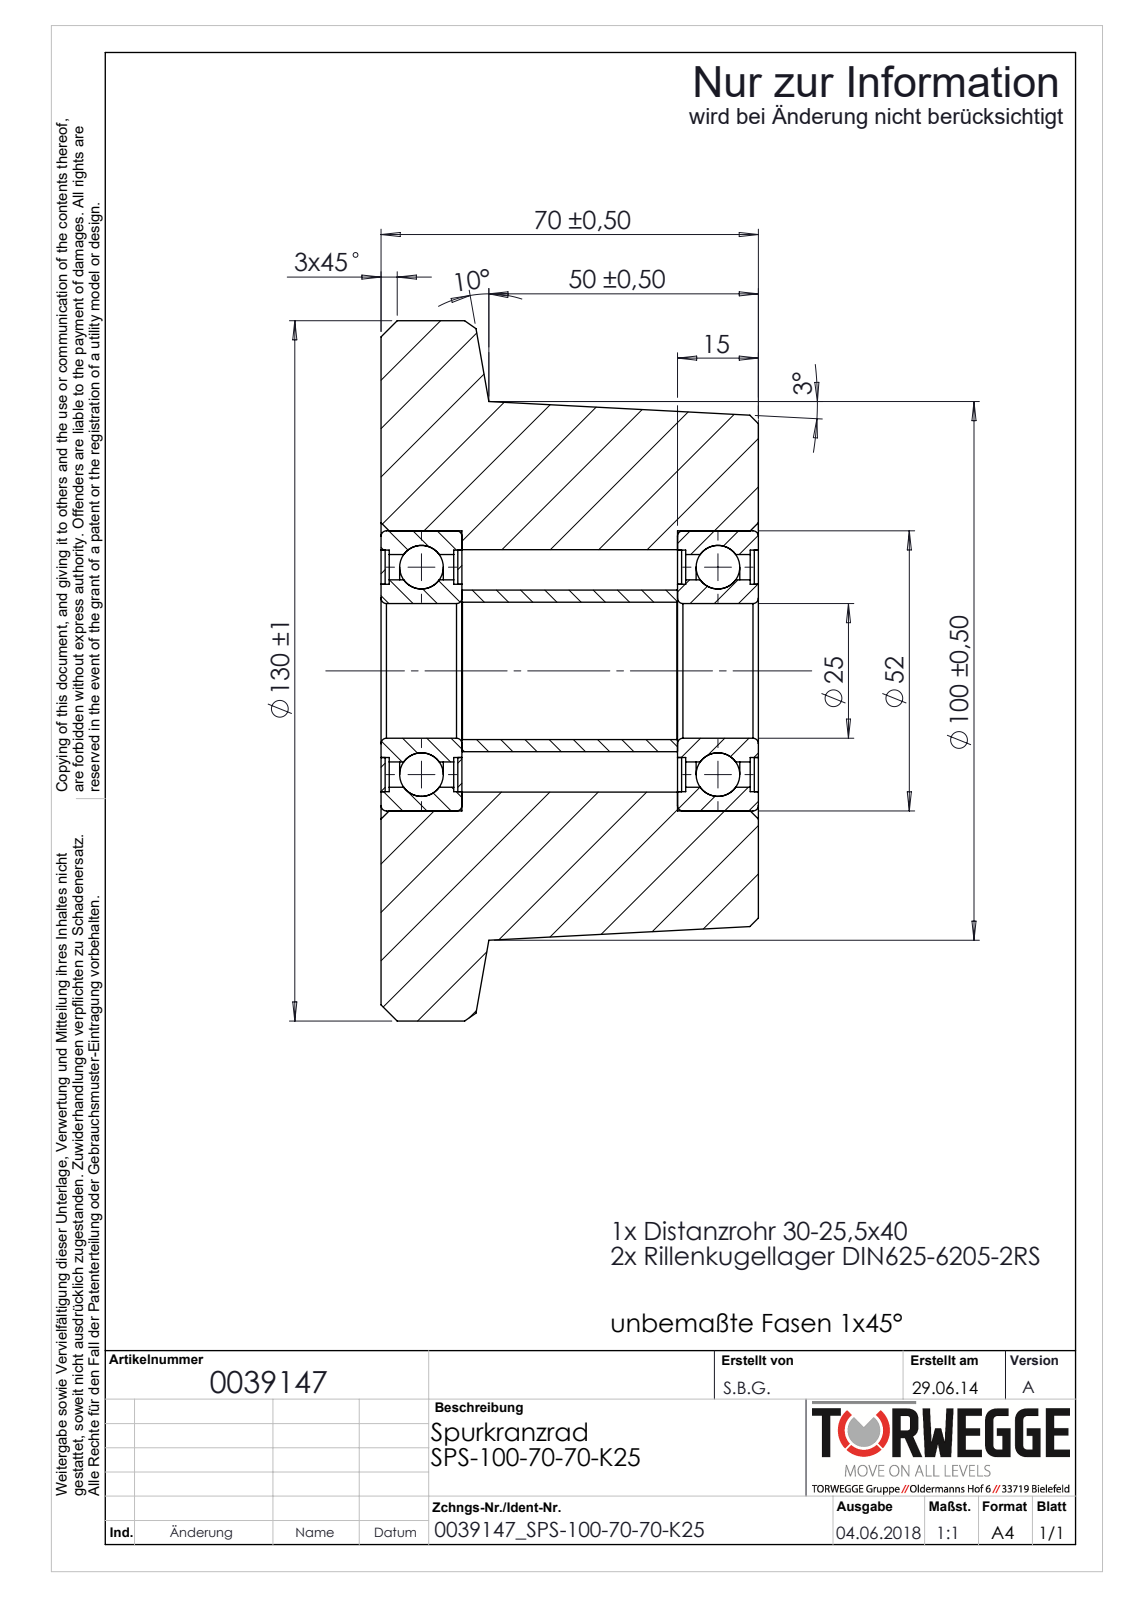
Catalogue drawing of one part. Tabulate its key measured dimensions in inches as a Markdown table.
| quantity | value |
| --- | --- |
| part name | 0039147_SPS-100-70-70-K25 |
| STEP written by | SolidWorks 2018 (AUTOMOTIVE_DESIGN) |
| units | inches |
| bodies | 12 solids, 156 faces (30 planar, 68 cylindrical, 58 other) |
| overall size | 5.118 × 5.118 × 2.756 |
| volume | 33.53 in³ |
| surface area | 144.6 in² |
| round holes (diameter × count) | 0.984 × 1, 1.004 × 1, 1.266 × 1, 1.701 × 1, 1.766 × 1, 1.772 × 1, 2.047 × 1 |
| round bosses / shafts (diameter × count) | 5.118 × 1, 1.331 × 1, 1.181 × 1 |
| main face-to-face distances | 2.165, 2.756, 0.591, 0.03, 0.561, 0.531, 1.575, 2.195, 2.135, 1.605 |
